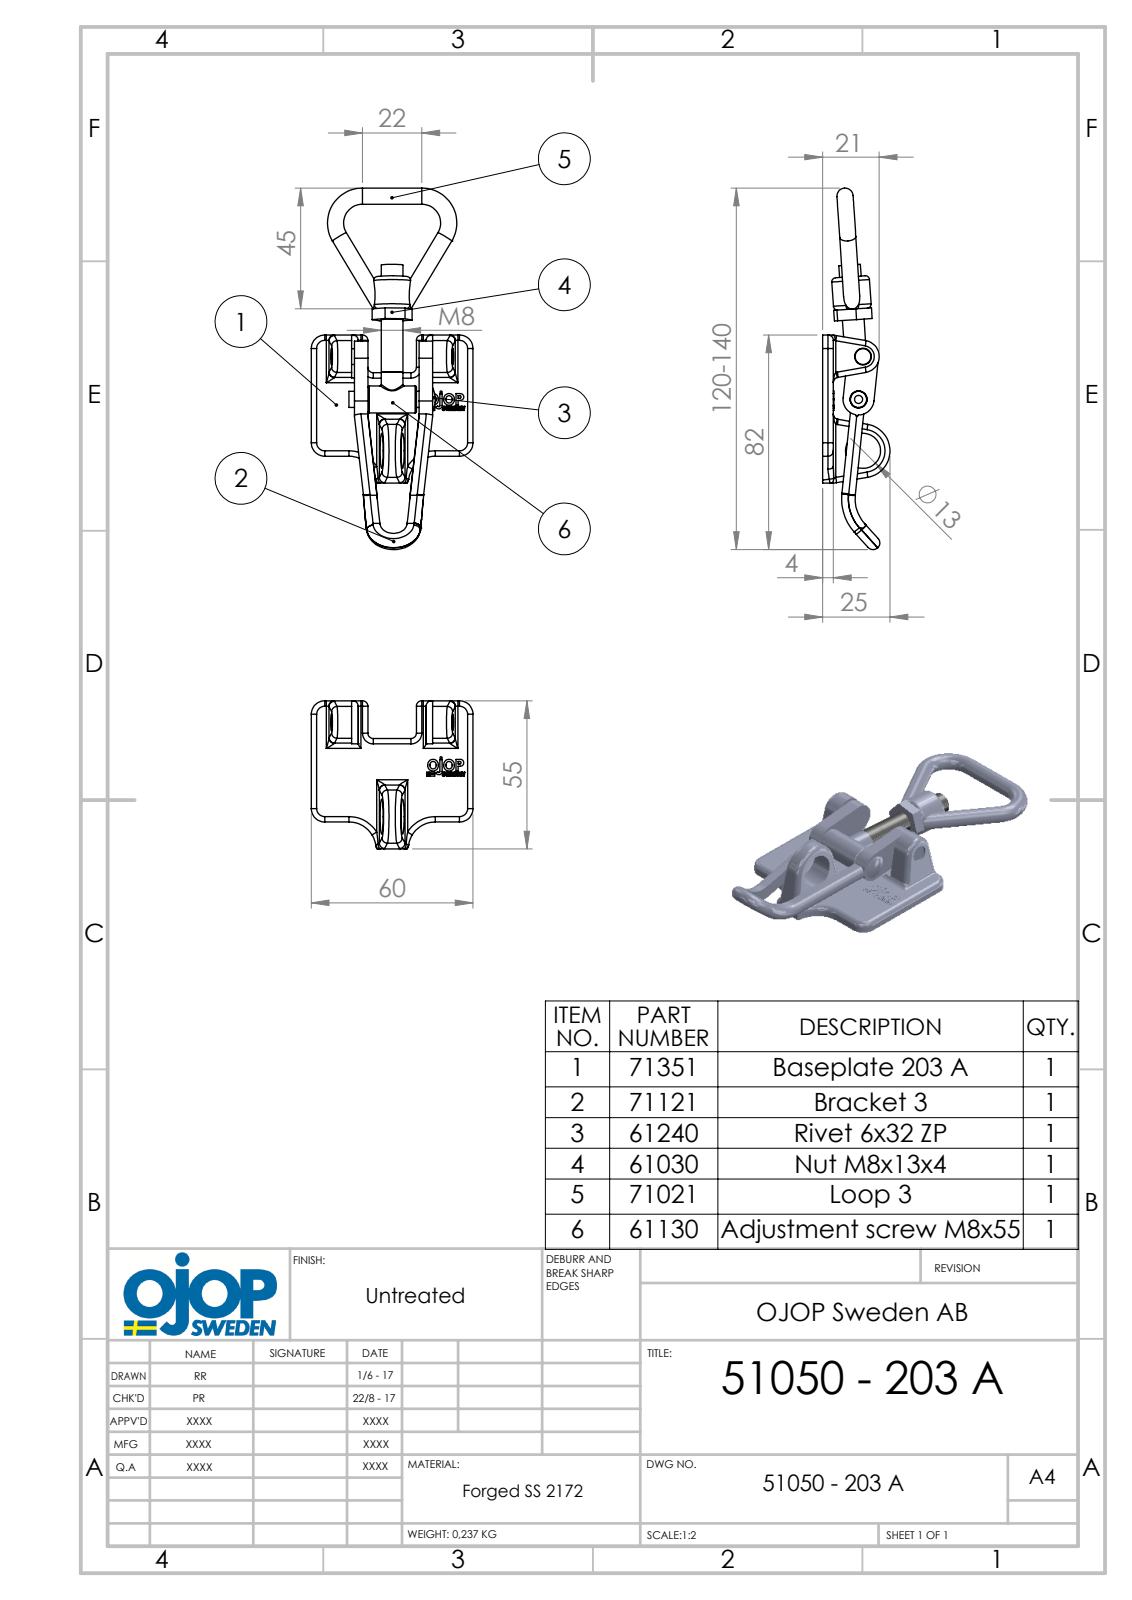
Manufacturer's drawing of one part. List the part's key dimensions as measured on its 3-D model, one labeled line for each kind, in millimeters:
Part name (STEP PRODUCT): Justerskruv M8; 51050 - 203 A; Ring 3; Mutter M8x13x4 (+3 more)
STEP written by: SolidWorks 2015 (AUTOMOTIVE_DESIGN)
Units: millimetres
Bodies: 6 solids, 270 faces (74 planar, 107 cylindrical, 89 other)
Overall size (bounding box): 137.51 × 60 × 25
Volume: 29 685 mm³ · Surface area: 18 830 mm²
Round holes (diameter × count): ⌀8.1 ×2, ⌀3 ×1, ⌀6.2 ×1, ⌀6.3 ×1, ⌀6.5 ×1, ⌀13 ×1
Round bosses / shafts (diameter × count): ⌀6 ×4, ⌀10 ×1, ⌀8.01 ×1, ⌀8 ×1, ⌀5.85 ×1
Partial cylindrical surfaces — rounded edges, fillets, slot ends (radius × count): R2 ×19, R1 ×10, R2.5 ×8, R5 ×5, R6.99 ×4, R10 ×3, R1.5 ×2, R6.15 ×2
Main face-to-face distances: 4, 5, 25, 20, 30, 1, 45, 18.58, 40, 15
Hole centre spacings: 16, 19.29, 35
